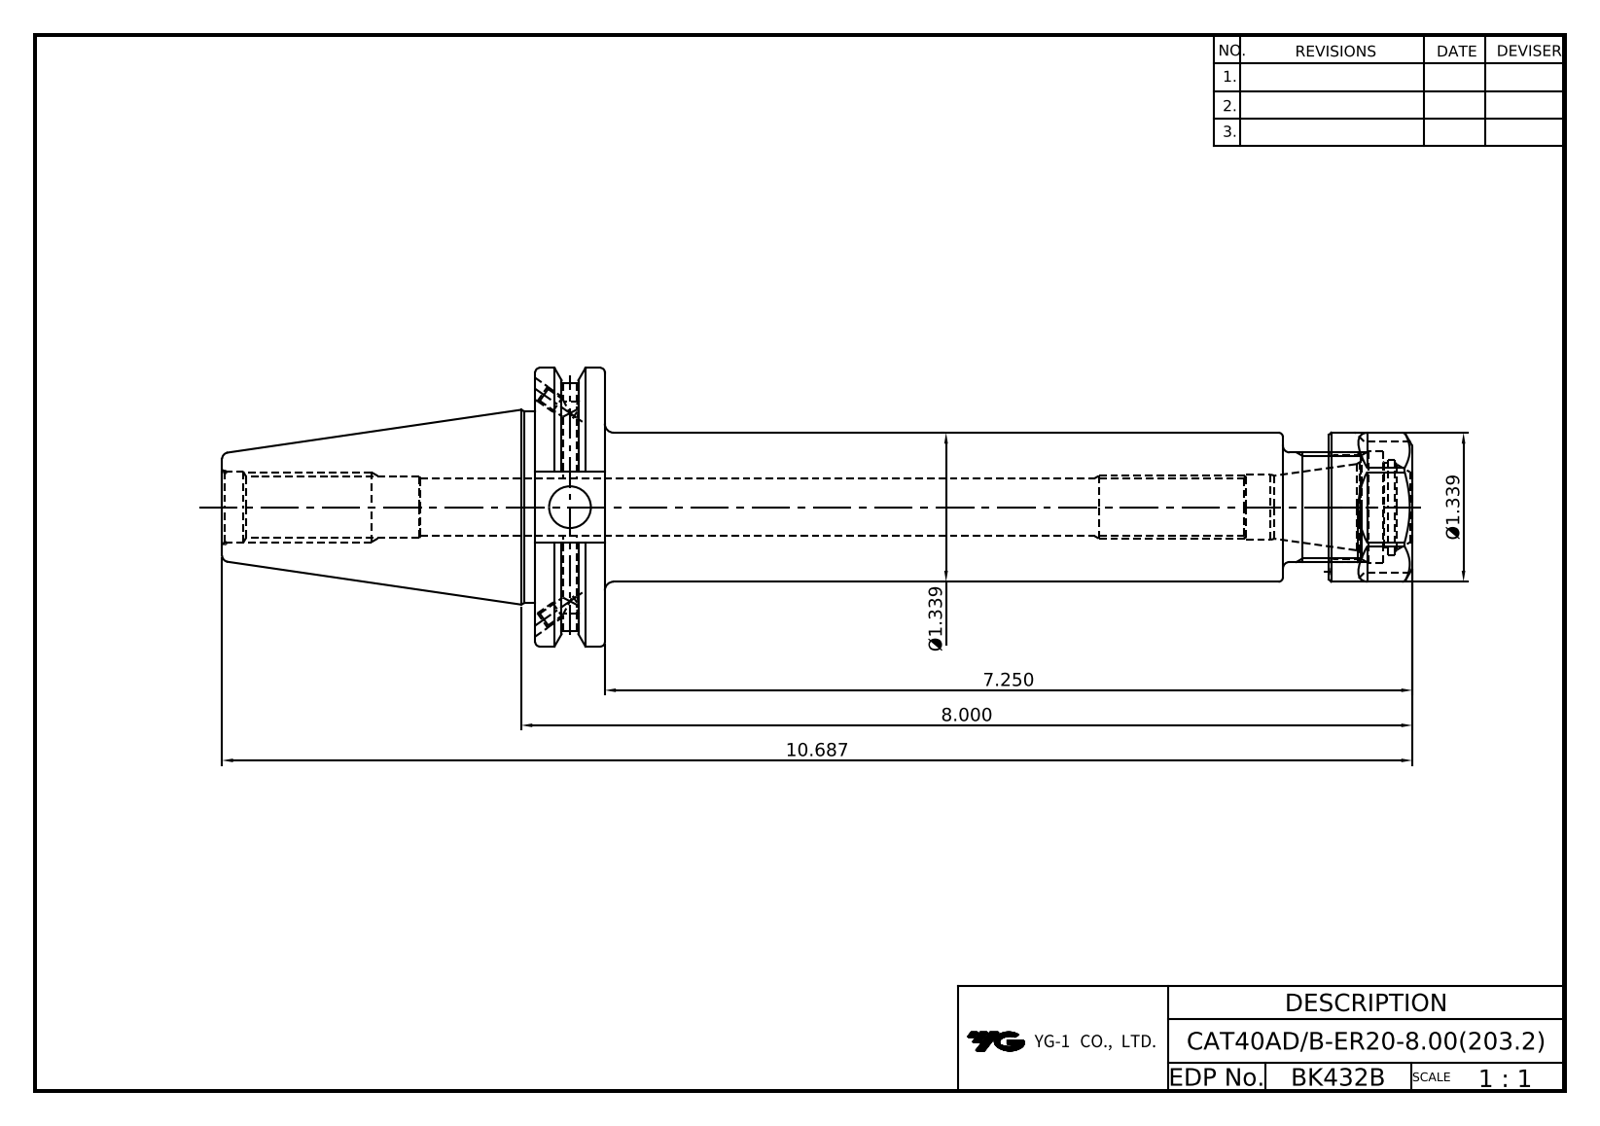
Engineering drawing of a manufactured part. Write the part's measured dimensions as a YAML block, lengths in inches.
part_name: "LO-CAT40ADB-ER20-8.00; ER20NUT"
step_written_by: "Autodesk Inventor 2025 (AUTOMOTIVE_DESIGN)"
units: inches
bodies: {solids: 2, faces: 119, planar: 56, cylindrical: 35, other: 28}
overall_size: [10.687, 2.5, 2.405]
volume: 14.32
surface_area: 78.7
round_holes:
  - {diameter: 0.128, count: 4}
  - {diameter: 0.157, count: 2}
  - {diameter: 0.165, count: 2}
  - {diameter: 0.375, count: 1}
  - {diameter: 0.495, count: 1}
  - {diameter: 0.527, count: 1}
  - {diameter: 0.587, count: 1}
  - {diameter: 0.63, count: 1}
  - {diameter: 0.642, count: 1}
  - {diameter: 0.724, count: 1}
  - {diameter: 0.857, count: 1}
  - {diameter: 0.925, count: 1}
round_bosses_or_shafts:
  - {diameter: 2.5, count: 1}
  - {diameter: 1.717, count: 1}
  - {diameter: 1.339, count: 1}
  - {diameter: 0.984, count: 1}
partial_cylinders:
  - {radius: 1.108, count: 1}
face_to_face_distances: [0.625, 1.181, 7.875, 7.25, 0.748, 7.127, 6.502, 7.611, 6.986, 0.484]
